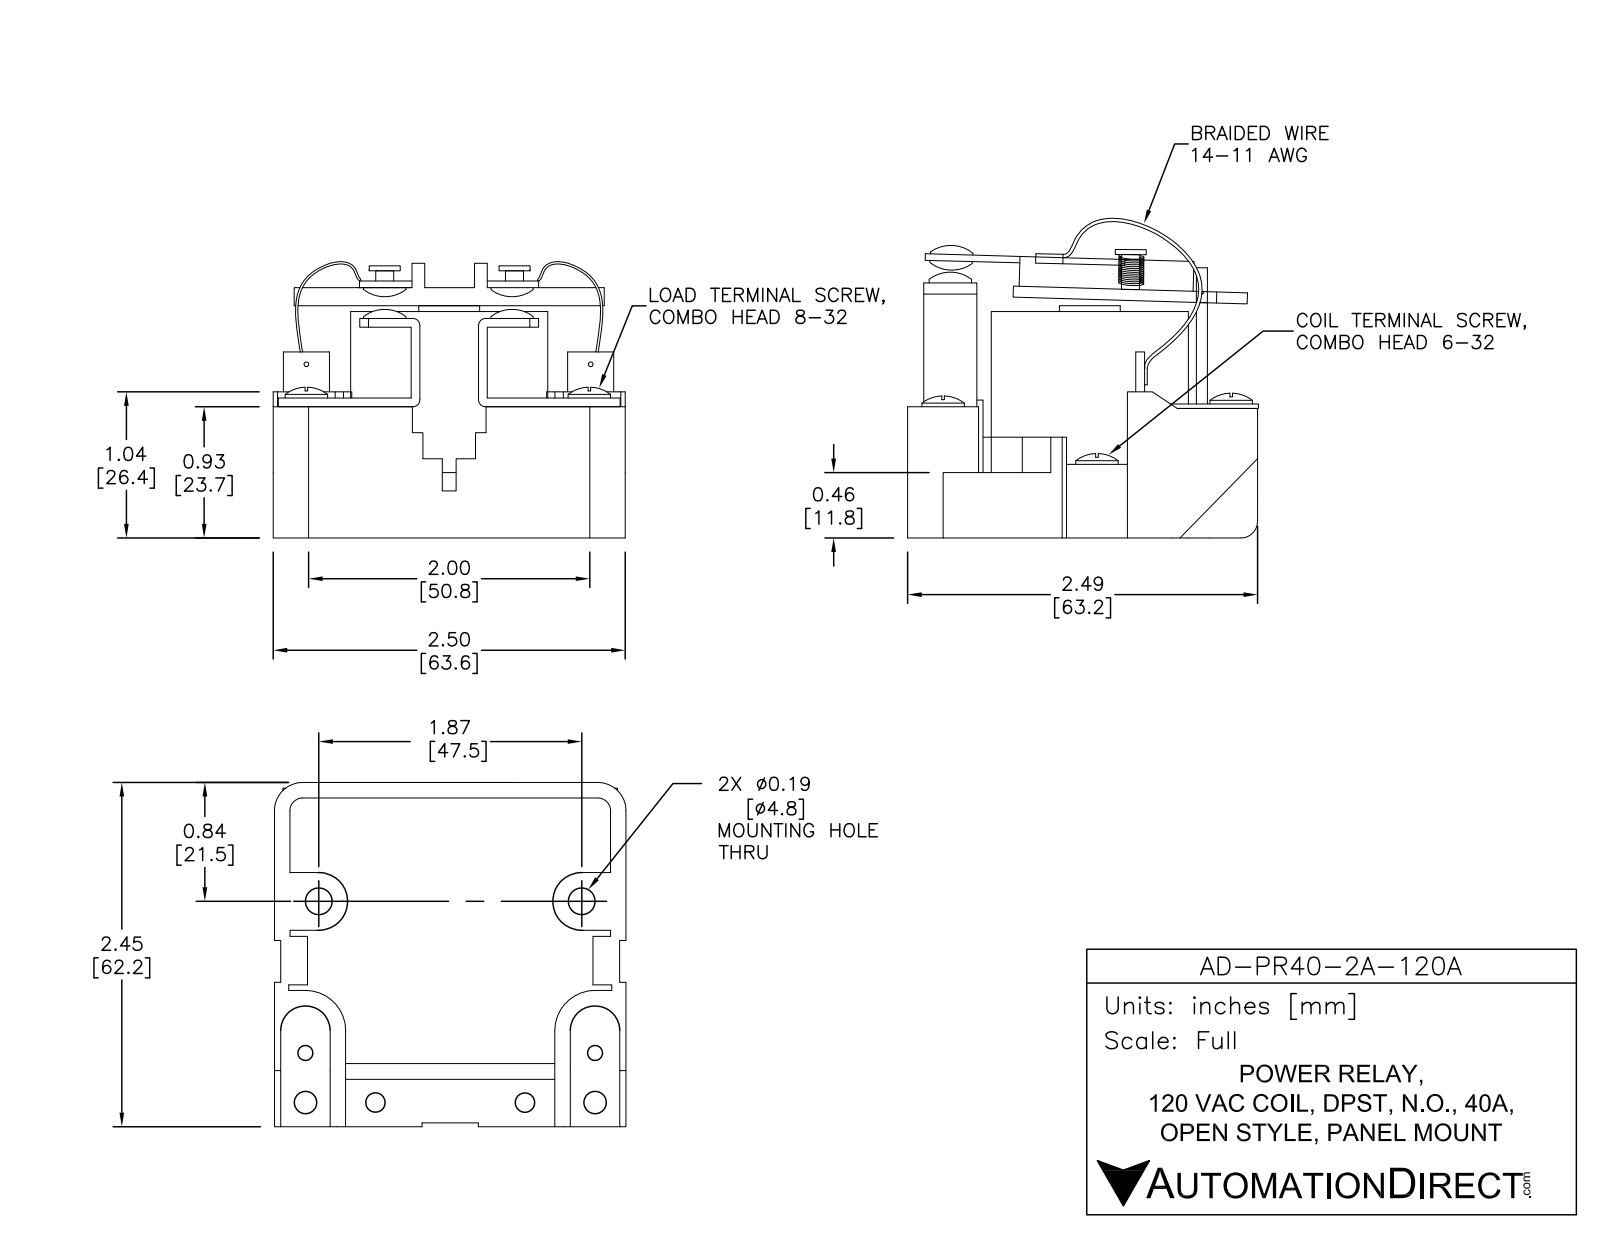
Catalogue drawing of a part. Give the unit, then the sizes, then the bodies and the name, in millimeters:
Units: millimetres
Overall size (bounding box): 65.57 × 64.94 × 54.85
Round holes (diameter × count): ⌀3.33 ×2, ⌀4.8 ×2, ⌀5 ×2, ⌀10 ×2, ⌀30 ×1
Round bosses / shafts (diameter × count): ⌀7.75 ×4, ⌀6.5 ×4, ⌀5.28 ×4, ⌀6.85 ×2, ⌀5.5 ×2, ⌀3.5 ×2, ⌀35.5 ×1, ⌀18 ×1
Partial cylindrical surfaces — rounded edges, fillets, slot ends (radius × count): R1 ×14, R0.75 ×10, R1.5 ×6, R3 ×5, R5 ×5, R0.38 ×4, R1.48 ×4, R1.51 ×4
Main face-to-face distances: 2, 48.05, 1, 4.5, 1.5, 36.25, 11.8, 6.5, 44.55, 3.5
Hole centre spacings: 10, 25.62, 25.71, 35.71, 48.85, 49.86, 29.25, 29.26
Volume: 96 384 mm³ · Surface area: 37 339 mm²
Bodies: 39 solids, 816 faces (555 planar, 167 cylindrical, 94 other)
Part name (STEP PRODUCT): AD-PR40-2A-120A
STEP written by: SolidWorks 2018 (AUTOMOTIVE_DESIGN)
